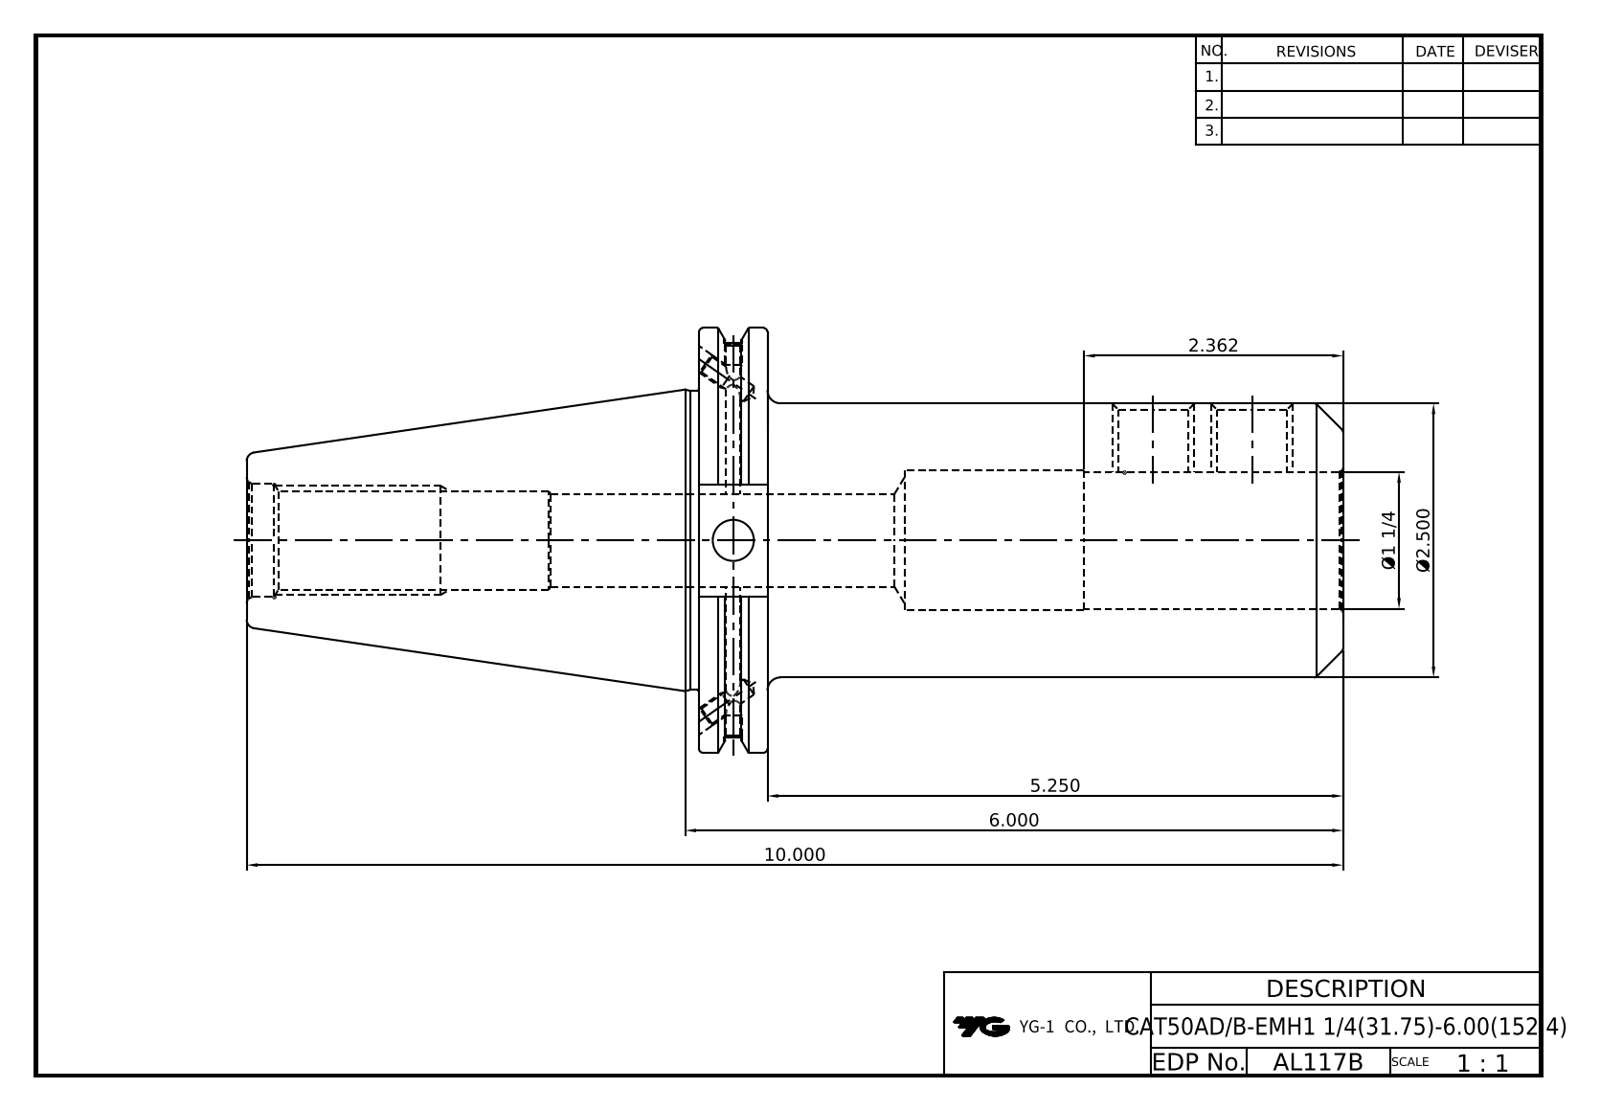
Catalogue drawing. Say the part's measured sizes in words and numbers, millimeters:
The part is named "LO-CAT50ADB-EMH31.75-152.4". Its 3-D file was written by "Autodesk Inventor 2025 (AUTOMOTIVE_DESIGN)". It is 1 solid with 89 faces: 39 planar, 27 cylindrical and 23 other. Overall it measures 254 by 98.42 by 94.69 millimeters. Its volume is 634 126 cubic millimeters and its surface area 83 542 square millimeters. Round holes: 2 of diameter 3.24, 2 of diameter 4.13, 2 of diameter 4.2, 2 of diameter 5, 2 of diameter 17.32, 1 of diameter 9.53, 1 of diameter 21.97, 1 of diameter 26.2, 1 of diameter 31.75, 1 of diameter 32.95. Round bosses or shafts: 1 of diameter 98.42, 1 of diameter 91.29, 1 of diameter 69.25, 1 of diameter 63.5. The main face-to-face distances are 15.88, 149.23, 133.35, 104.77, 120.65, 254, 152.4, 47.63, 31.75, 101.6. The hole center spacings are 22.86.
